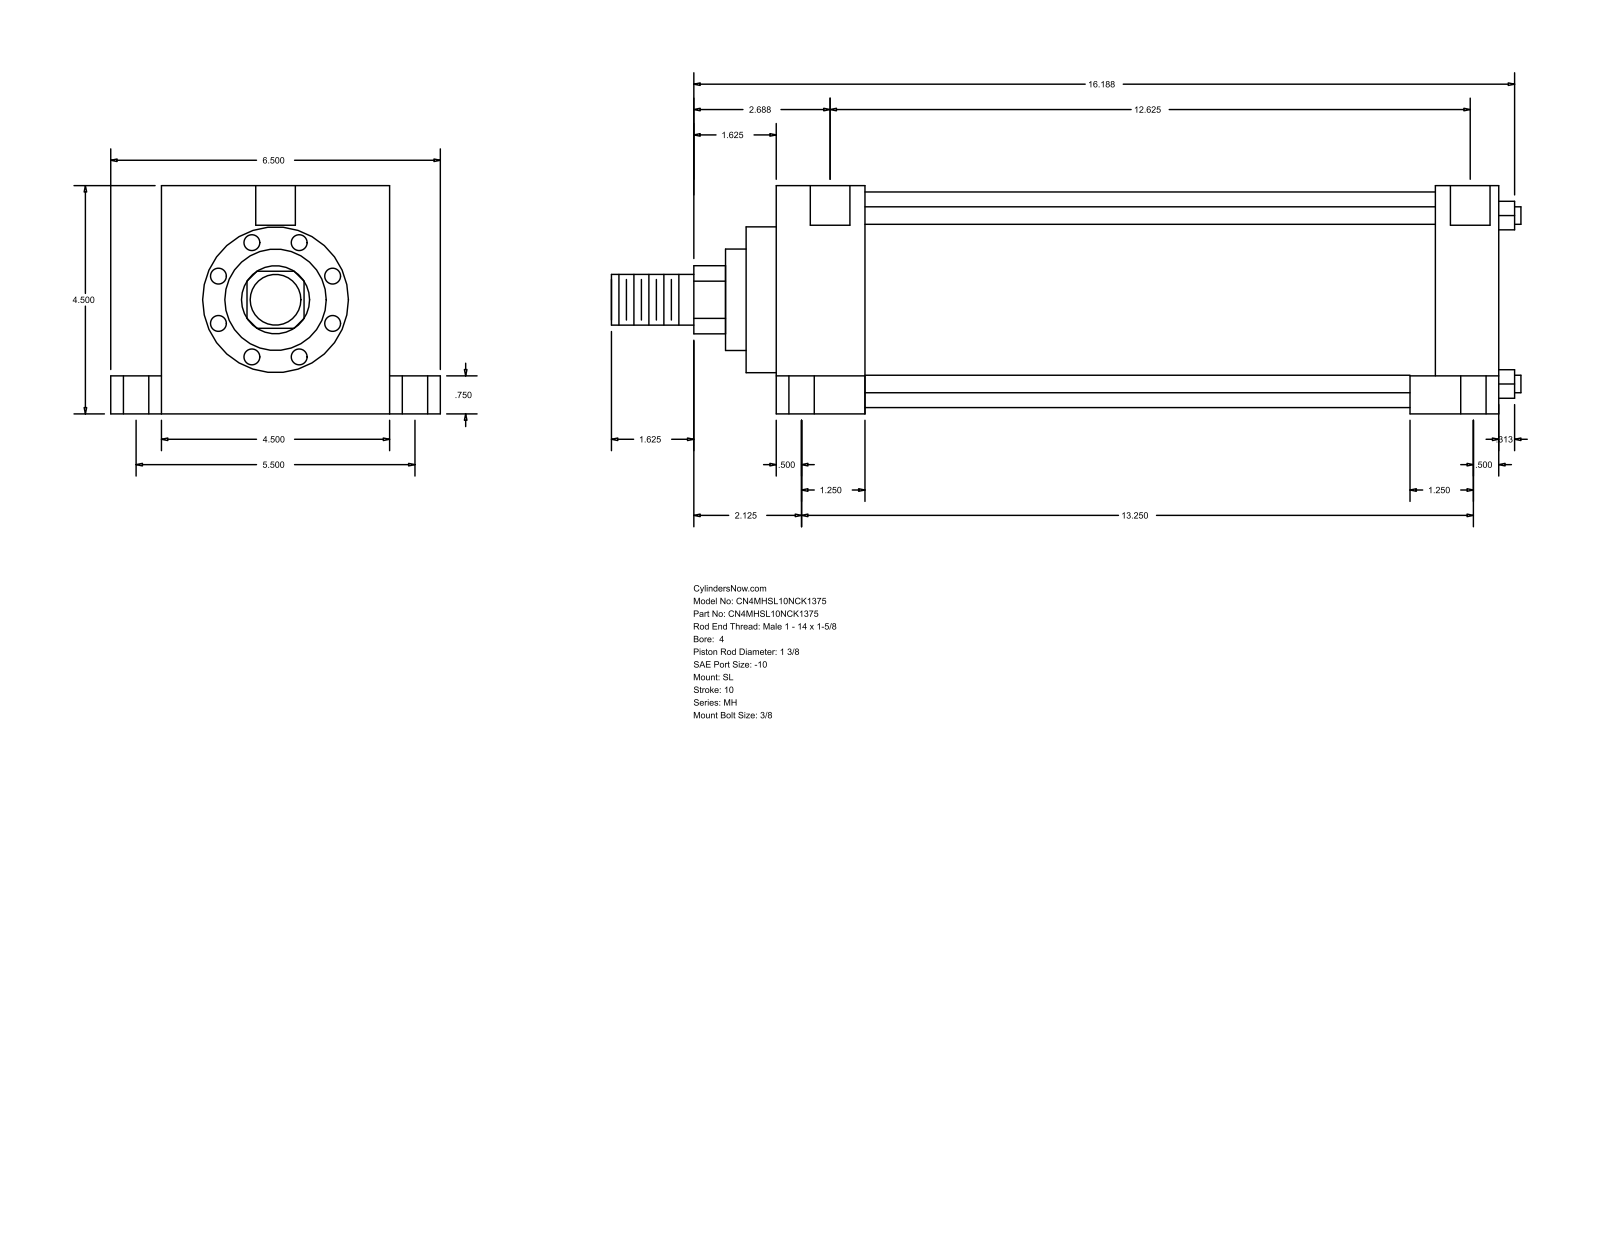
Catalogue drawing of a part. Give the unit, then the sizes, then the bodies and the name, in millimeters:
Units: millimetres
Overall size (bounding box): 455.61 × 165.1 × 114.3
Round holes (diameter × count): ⌀8.73 ×4, ⌀12.7 ×4, ⌀19.05 ×4, ⌀19.84 ×2
Round bosses / shafts (diameter × count): ⌀8.76 ×4, ⌀107.95 ×1, ⌀73.03 ×1, ⌀50.8 ×1, ⌀34.92 ×1, ⌀25.4 ×1
Partial cylindrical surfaces — rounded edges, fillets, slot ends (radius × count): R17.06 ×1
Main face-to-face distances: 114.3, 361.96, 44.45, 317.51, 330.21, 285.76, 31.75, 25.4, 139.7, 19.05
Hole centre spacings: 69.85, 69.87, 70.99, 71.29, 139.7, 323.85, 329.74, 331.3
Bodies: 0 solids, 110 faces (77 planar, 33 cylindrical, 0 other)
Part name (STEP PRODUCT): MH_SL__0400_1.375
STEP written by: GSSL Pune (CONFIG_CONTROL_DESIGN)
